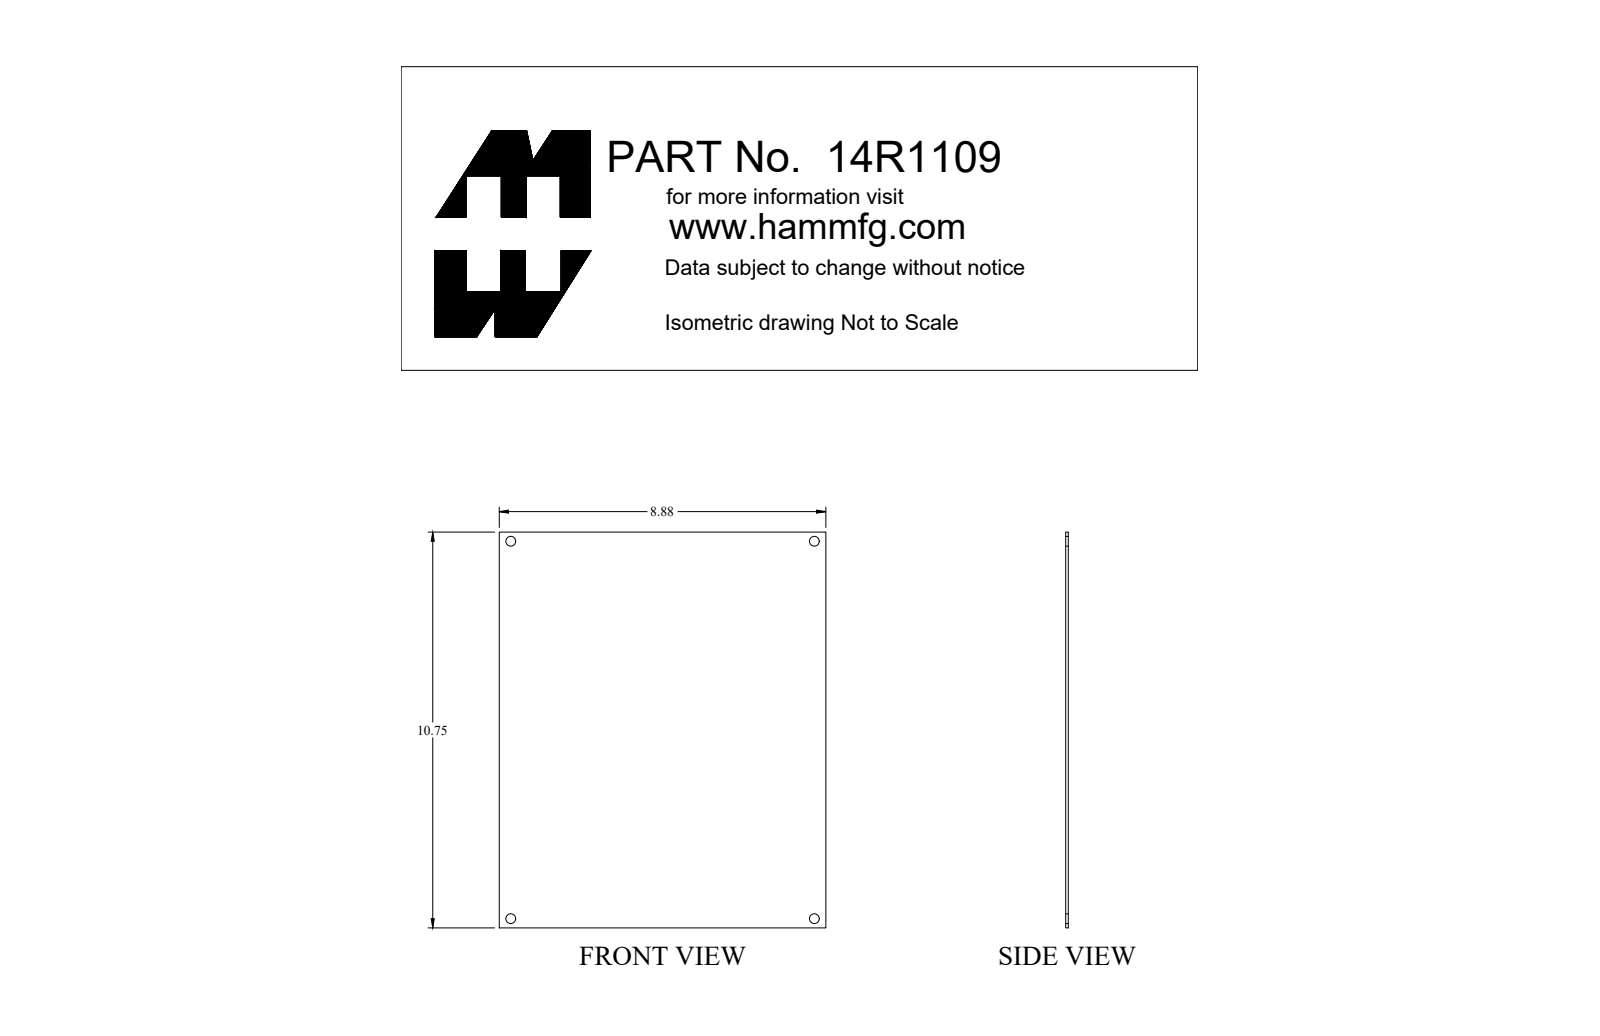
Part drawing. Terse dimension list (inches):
name: 14R1109
written by: SolidWorks 2018 (AUTOMOTIVE_DESIGN)
unit: in
bodies: 1 solid, 10 faces (6 planar, 4 cylindrical, 0 other)
size: 10.75 × 8.875 × 0.072
volume: 6.853 in³; area: 193.4 in²
holes: 4× ⌀0.265
face distances: 0.072, 8.875, 10.75
hole spacings: 8.25, 10.25, 13.158
